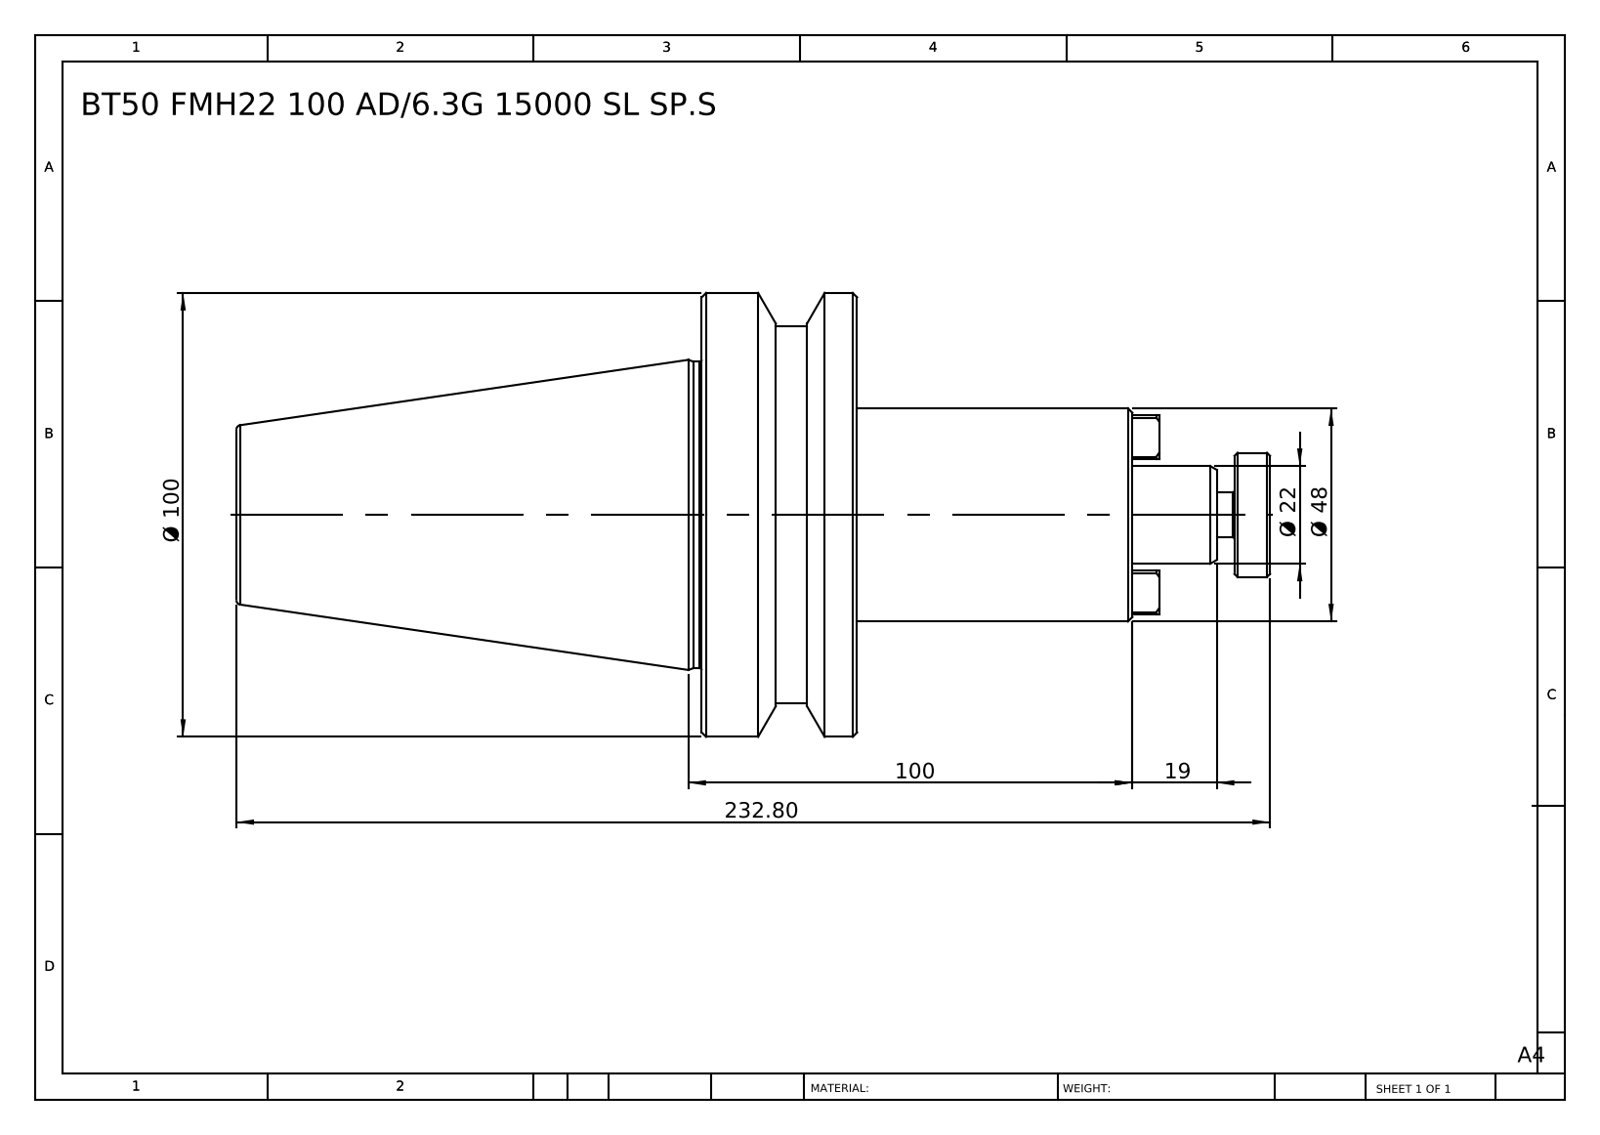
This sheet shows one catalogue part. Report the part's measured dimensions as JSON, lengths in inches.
{"part_name": "BT50 FMH22 100 AD-6.3G 15000 SL SP.S", "step_written_by": "SolidWorks 2014 (CONFIG_CONTROL_DESIGN)", "units": "inches", "bodies": {"solids": 1, "faces": 77, "planar": 35, "cylindrical": 16, "other": 26}, "overall_size": [9.165, 3.937, 3.937], "volume_in3": 38.8, "surface_area_in2": 88.62, "round_bosses_or_shafts": [[3.937, 1], [3.346, 1], [2.717, 1], [1.89, 1], [1.102, 1], [0.866, 1], [0.394, 1]], "face_to_face_distances": [1.378, 5.504, 4.126, 2.441, 3.819, 7.945, 1.22, 3.661, 5.039, 9.165]}
